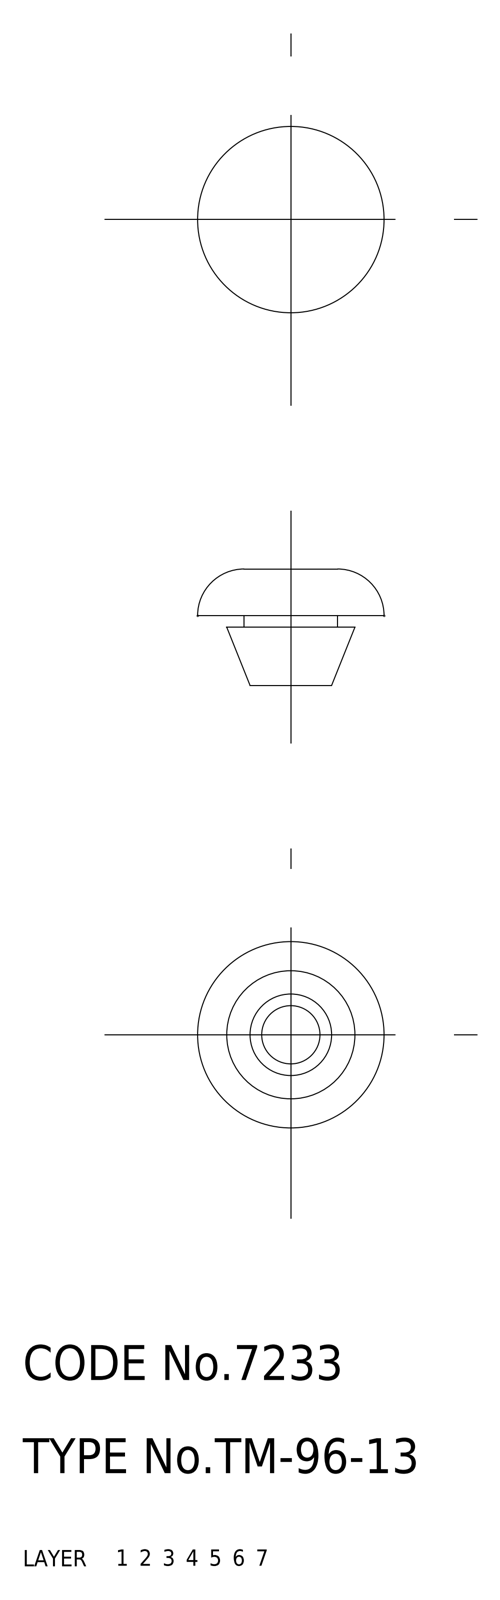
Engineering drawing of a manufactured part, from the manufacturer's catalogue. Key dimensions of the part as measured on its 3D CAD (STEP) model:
Part name (STEP PRODUCT): cushion
STEP written by: CADfix (AUTOMOTIVE_DESIGN)
Units: millimetres
Bodies: 1 solid, 13 faces (0 planar, 0 cylindrical, 13 other)
Overall size (bounding box): 16 × 16 × 10
Volume: 908 mm³ · Surface area: 815 mm²
